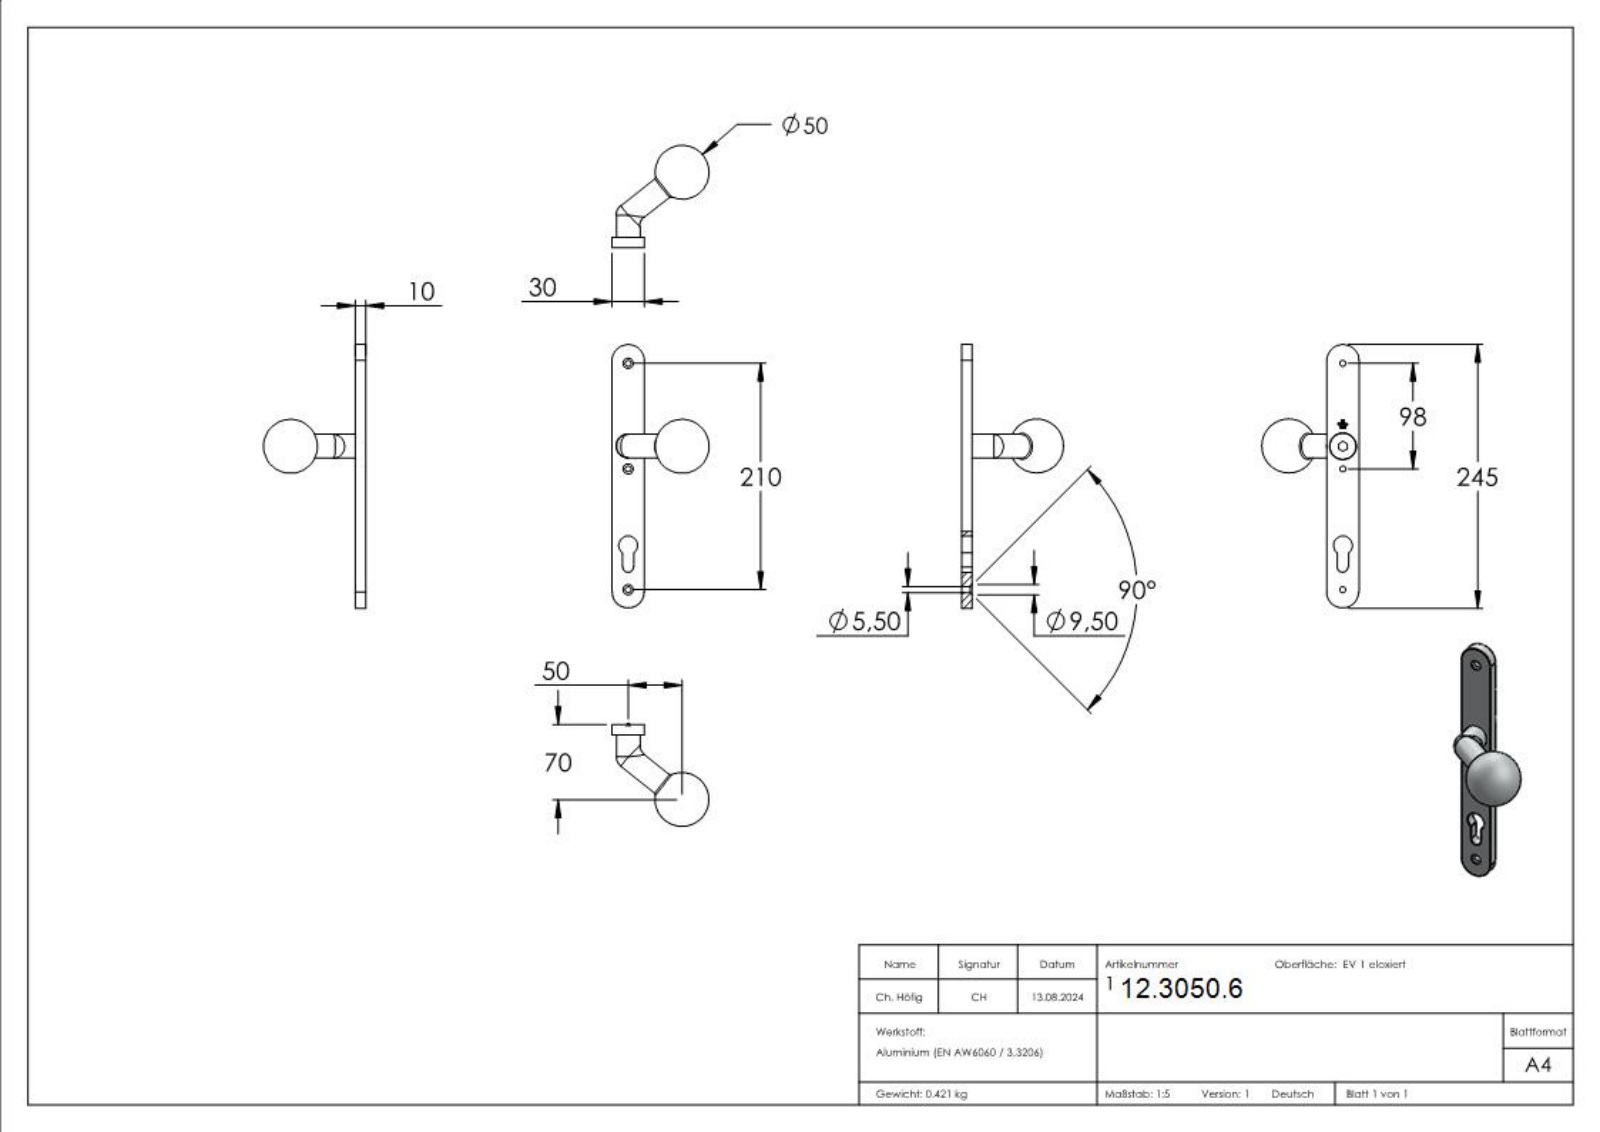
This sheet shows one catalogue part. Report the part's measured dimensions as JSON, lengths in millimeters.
{"part_name": "15661 Teil1_15661 Teil1; DIN 7991 Konfig_M12x20; 15661; 15661 Teil2_15661 Teil2", "step_written_by": "SolidWorks 2018 (CONFIG_CONTROL_DESIGN)", "units": "millimeters", "bodies": {"solids": 4, "faces": 280, "planar": 144, "cylindrical": 25, "other": 111}, "overall_size": [245, 113, 90], "volume_mm3": 286843, "surface_area_mm2": 51485, "round_holes": [[5.5, 3], [10.2, 1], [17.5, 1], [25, 1]], "round_bosses_or_shafts": [[22, 3], [24, 1], [19.75, 1], [12, 1]], "partial_cylinders_radius": [[0.75, 2], [15, 2], [5.25, 1]], "face_to_face_distances": [10, 30, 4, 6, 6.5, 3.5, 2.5, 9.75, 20.25, 5], "hole_center_spacings": [21, 41, 71, 77, 92, 98, 112, 133]}
